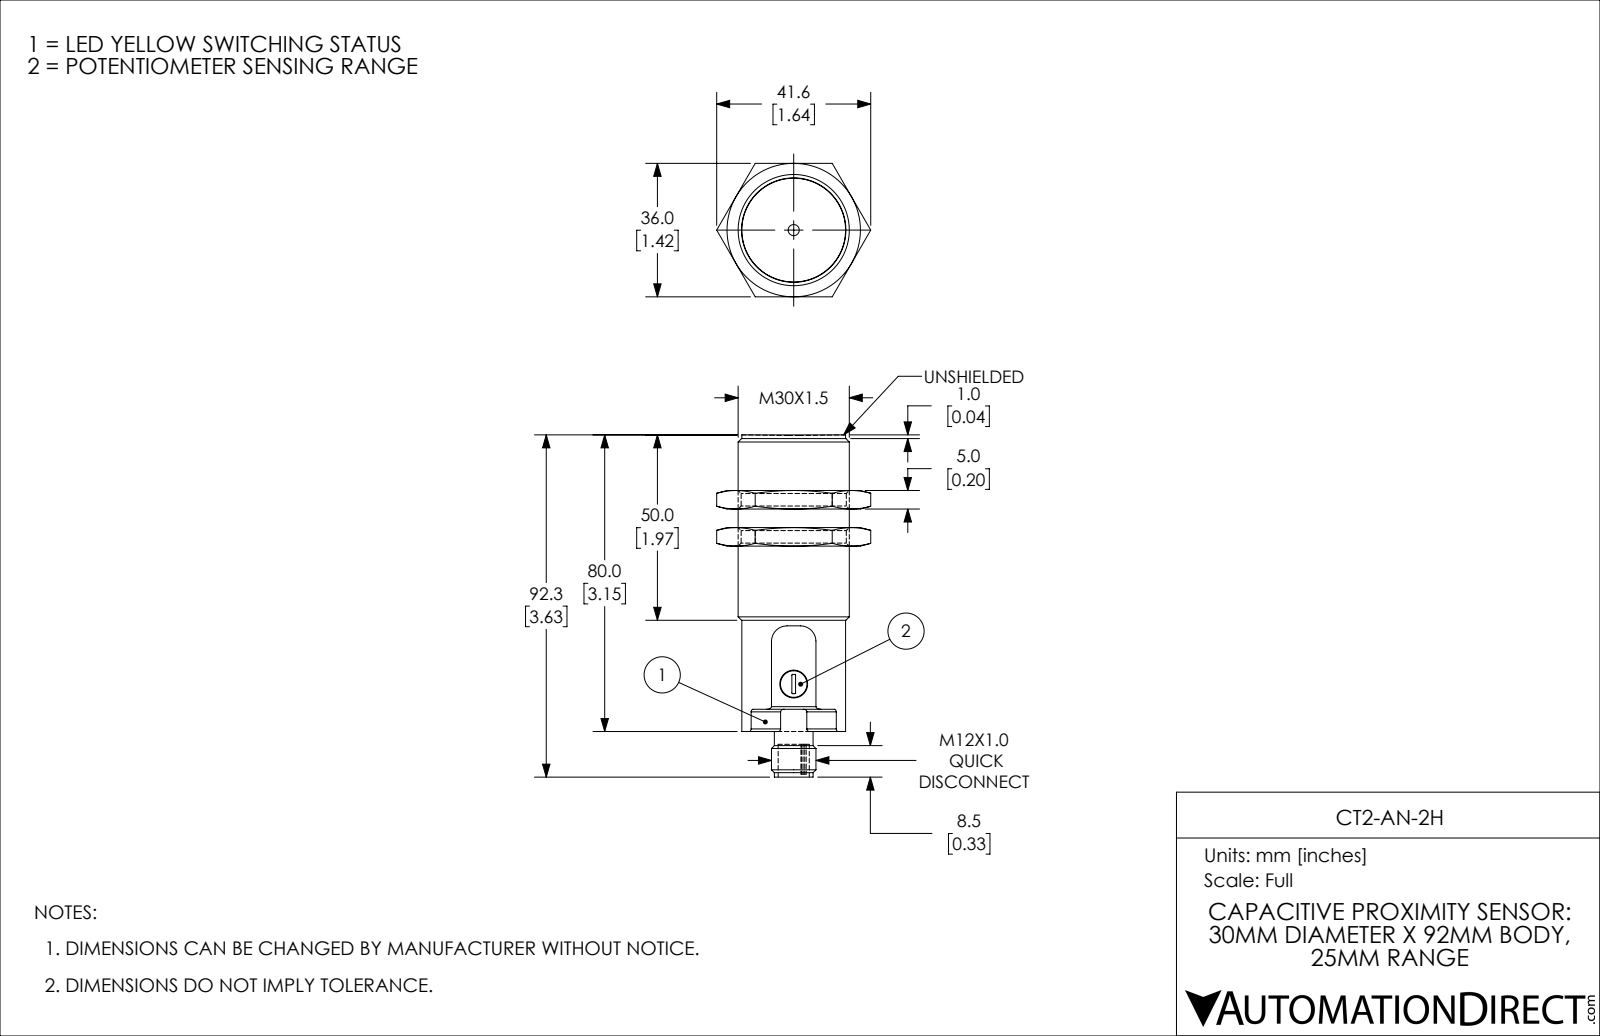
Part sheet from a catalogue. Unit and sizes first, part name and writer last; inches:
Units: inches
Overall size (bounding box): 3.634 × 1.637 × 1.417
Round holes (diameter × count): ⌀0.331 ×1, ⌀1.117 ×1
Round bosses / shafts (diameter × count): ⌀1.181 ×1, ⌀1.102 ×1, ⌀0.472 ×1, ⌀0.411 ×1, ⌀0.295 ×1
Partial cylindrical surfaces — rounded edges, fillets, slot ends (radius × count): R0.008 ×4, R0.028 ×3, R0.165 ×2, R0.024 ×1
Main face-to-face distances: 0.197, 0.394, 1.417, 2.165, 2.362, 1.969, 2.559, 0.591, 1.207, 0.211
Hole centre spacings: 0.163
Volume: 3.557 in³ · Surface area: 20.39 in²
Bodies: 3 solids, 92 faces (35 planar, 22 cylindrical, 35 other)
Part name (STEP PRODUCT): CT2-AN-2H
STEP written by: SolidWorks 2018 (AUTOMOTIVE_DESIGN)
